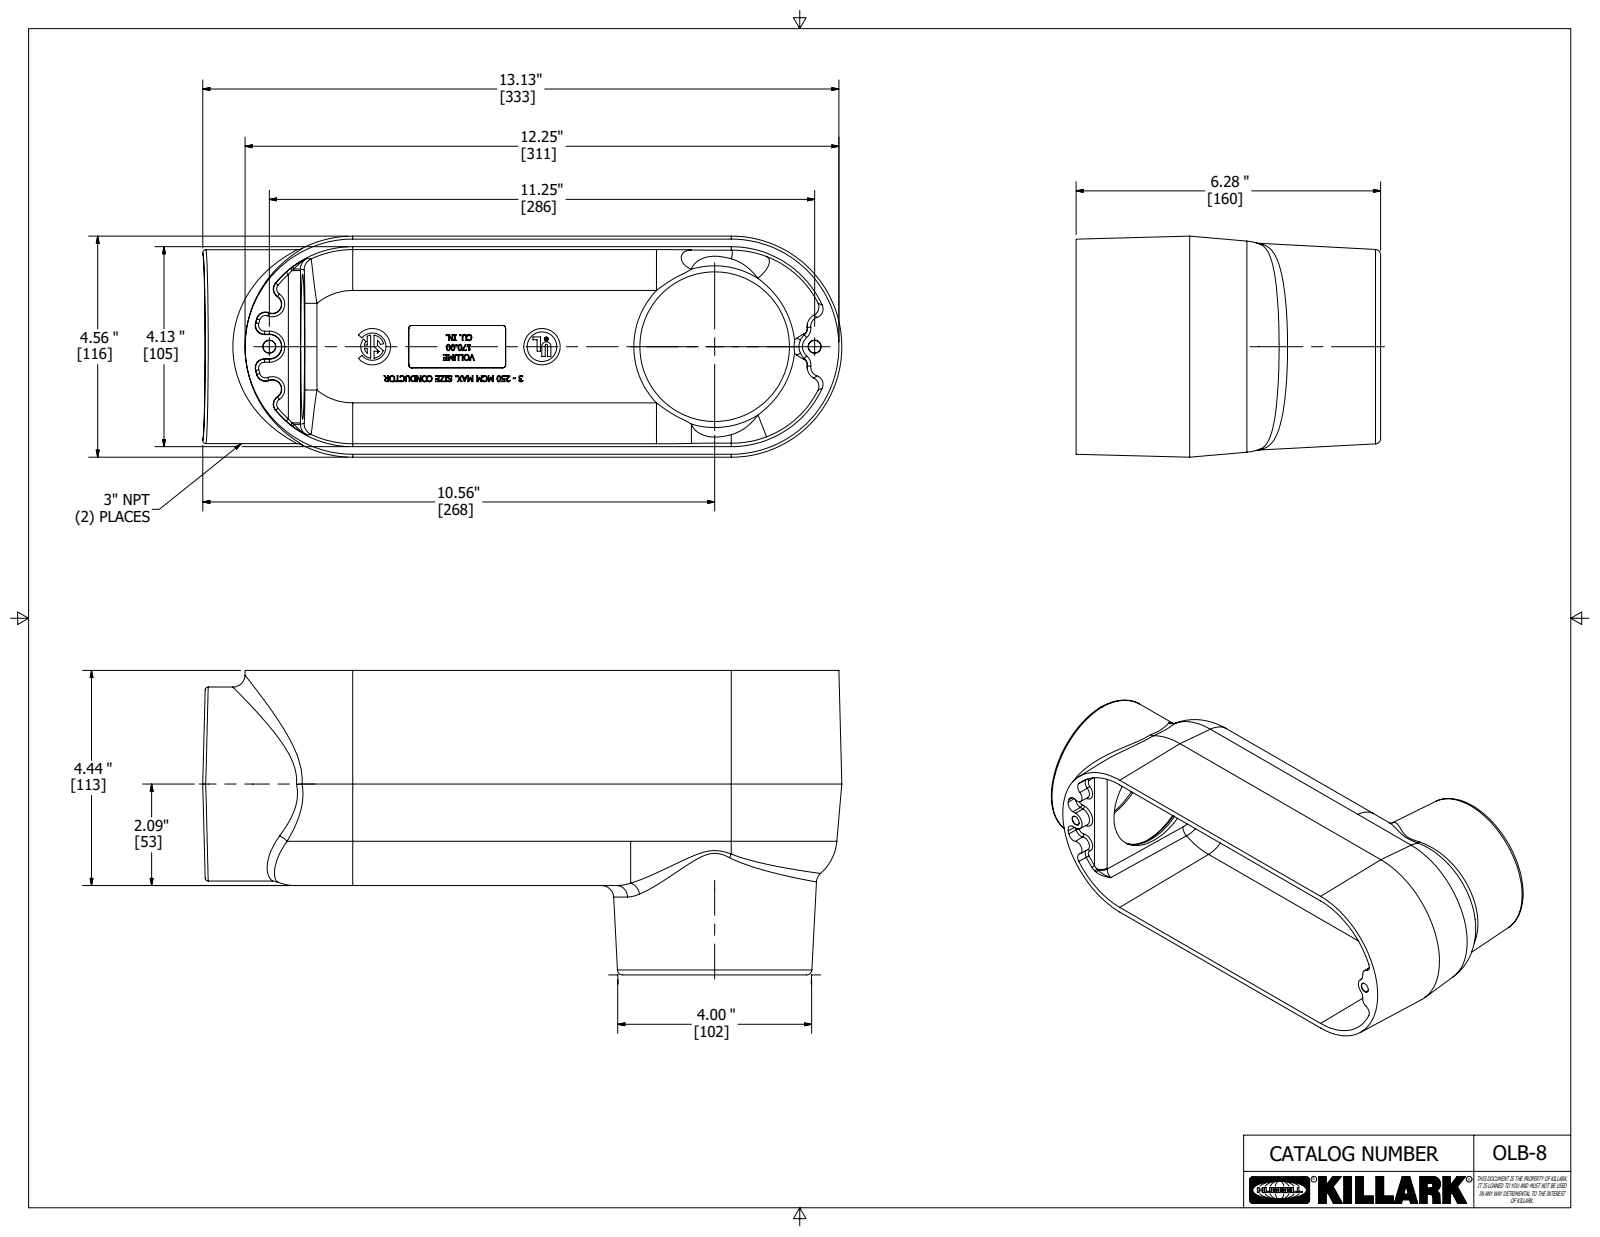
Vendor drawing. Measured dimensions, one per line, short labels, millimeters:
name: 17325-3
written by: Autodesk Inventor 2018 (AUTOMOTIVE_DESIGN)
unit: mm
bodies: 1 solid, 972 faces (528 planar, 40 cylindrical, 404 other)
size: 334.9 × 159.5 × 115.8
volume: 768 400 mm³; area: 242 800 mm²
holes: 2× ⌀6.6, 1× ⌀1.8, 1× ⌀15.5
bosses: 1× ⌀101.6, 1× ⌀19.1, 1× ⌀2.1
rounds: 10× R1.6, 2× R6.4, 2× R25.4, 1× R0.2, 1× R0.3, 1× R0.6, 1× R2.4, 1× R4.3
face distances: 4, 112.7, 108.7, 0.4, 4.3, 108.4, 3.2, 0.8, 3.6, 111.9
hole spacings: 142.9, 4.6, 140.6, 145.2, 285.8
